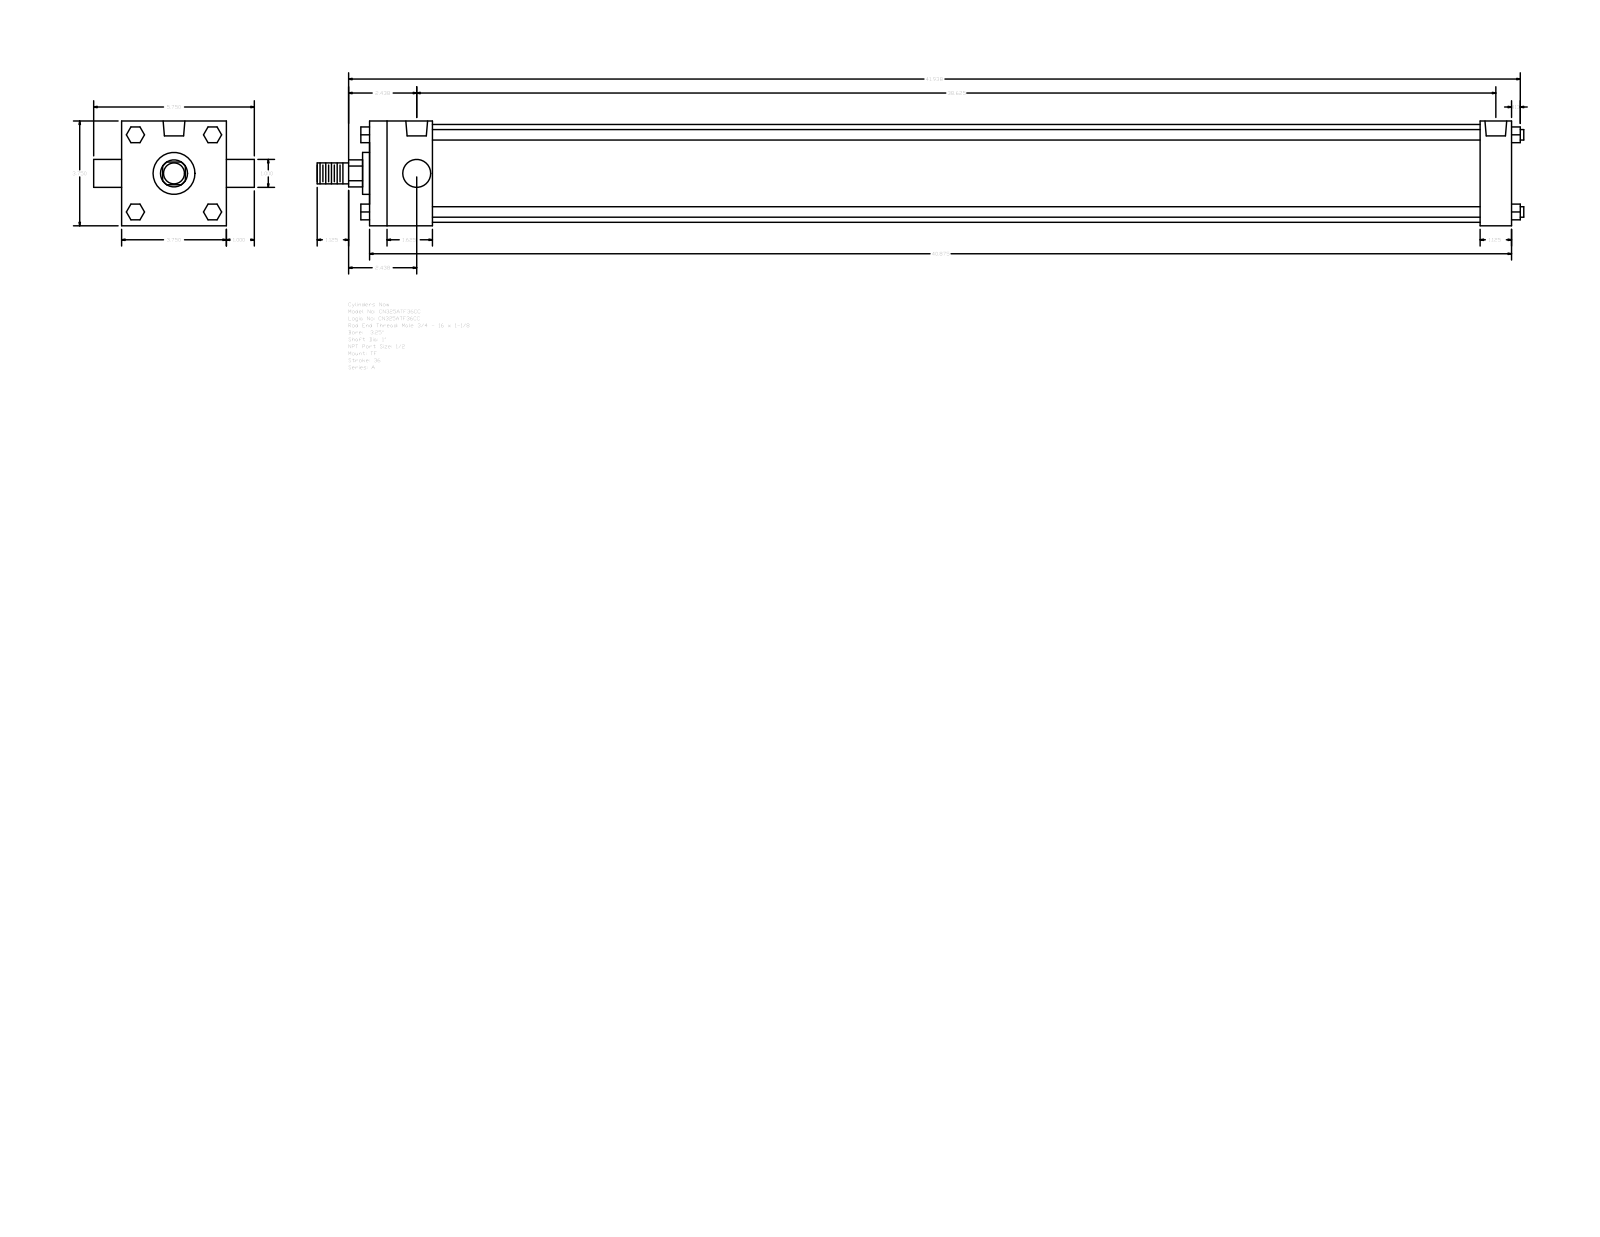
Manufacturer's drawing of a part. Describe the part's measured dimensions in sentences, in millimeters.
The part is named "A_TF__0325_1". Its 3-D file was written by "GSSL Pune (CONFIG_CONTROL_DESIGN)". It is 0 solids with 120 faces: 92 planar, 28 cylindrical and 0 other. Overall it measures 1096.96 by 146.05 by 95.25 millimeters. Round holes: 3 of diameter 8.73, 2 of diameter 19.77. Round bosses or shafts: 4 of diameter 9.53, 2 of diameter 25.4, 1 of diameter 88.9, 1 of diameter 38.1, 1 of diameter 19.05. Partial cylindrical surfaces (rounded edges, fillets, slot ends): 1 of radius 12.29. The main face-to-face distances are 95.24, 1038.23, 57.15, 1009.65, 952.5, 981.08, 28.58, 14.28, 35.05, 60.71. The hole center spacings are 3.18, 977.9, 974.72, 981.08.
